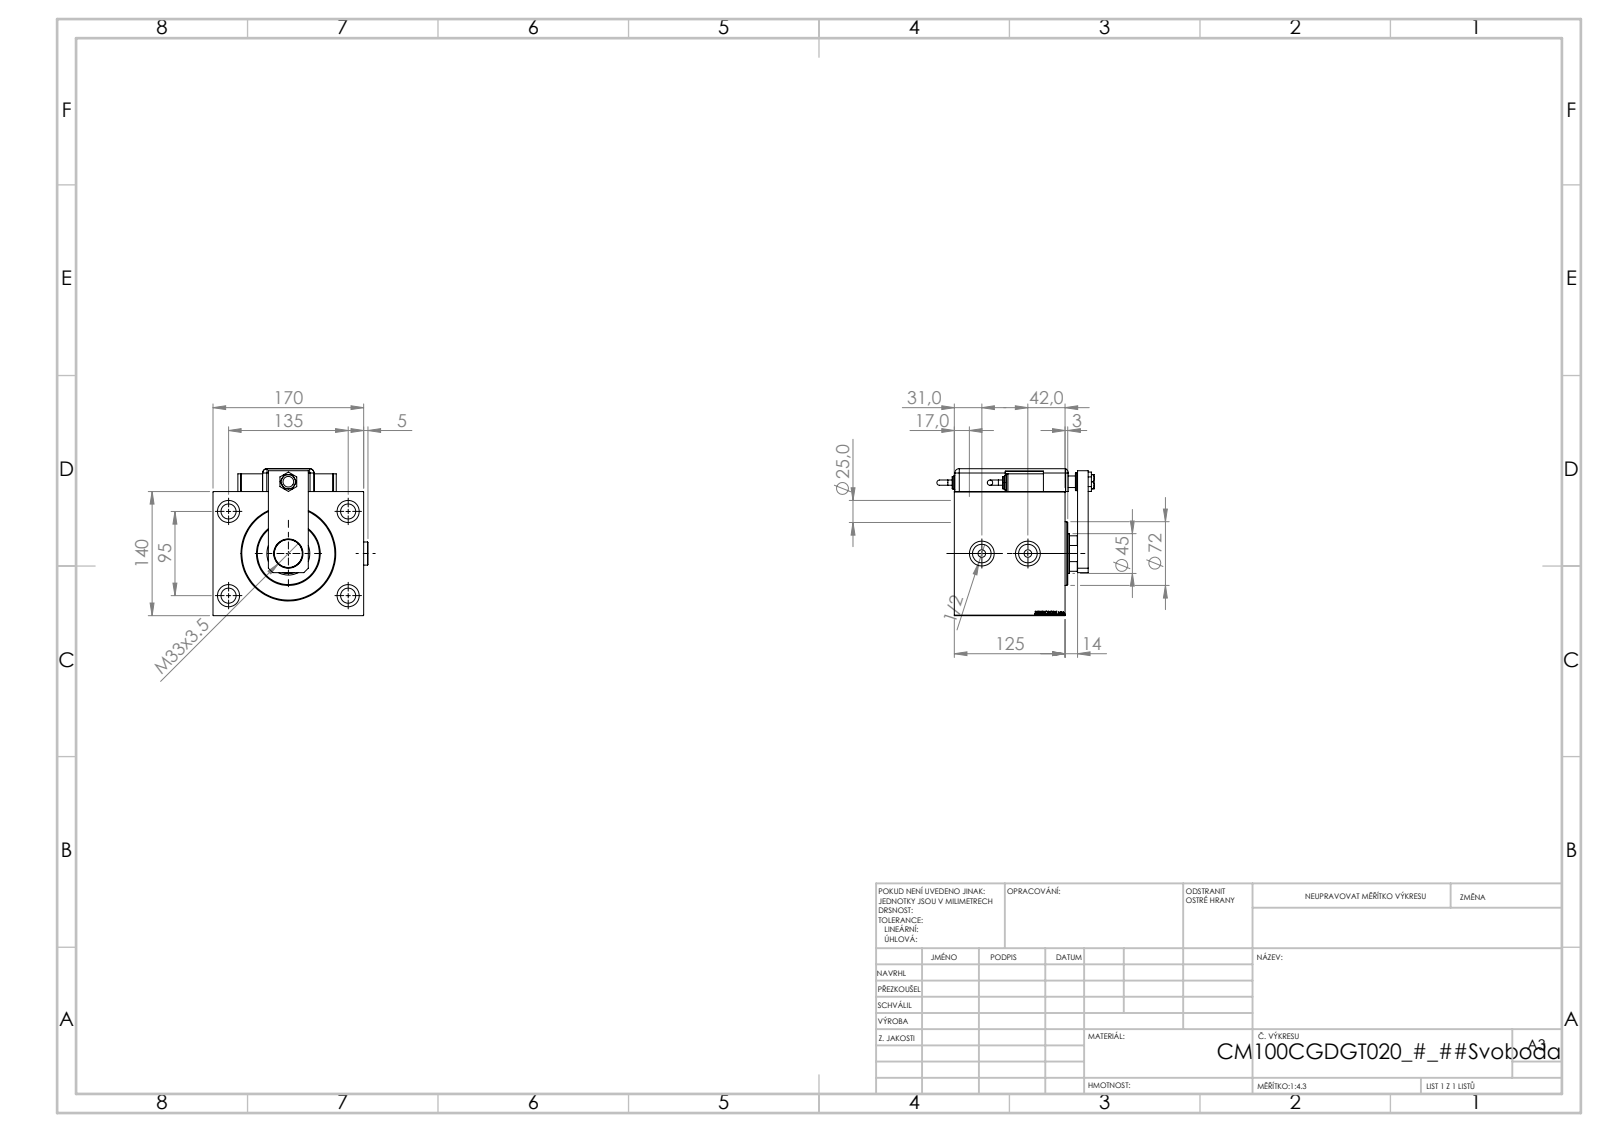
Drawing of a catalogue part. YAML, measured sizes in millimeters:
part_name: "SWITCH Q; V450CM_C_Body; V450CM_VC_B; TYC (+8 more)"
step_written_by: "SolidWorks 2019 (CONFIG_CONTROL_DESIGN)"
units: millimeters
bodies: {solids: 15, faces: 1301, planar: 649, cylindrical: 131, other: 521}
overall_size: [177.66, 174.9, 165.8]
volume: 2923000
surface_area: 306197
round_holes:
  - {diameter: 17, count: 4}
  - {diameter: 25, count: 4}
  - {diameter: 4, count: 2}
  - {diameter: 8, count: 2}
  - {diameter: 8.5, count: 2}
  - {diameter: 20.96, count: 2}
  - {diameter: 28, count: 2}
  - {diameter: 12, count: 1}
  - {diameter: 13, count: 1}
  - {diameter: 14, count: 1}
  - {diameter: 31.5, count: 1}
  - {diameter: 33, count: 1}
round_bosses_or_shafts:
  - {diameter: 20, count: 3}
  - {diameter: 26, count: 2}
  - {diameter: 16, count: 2}
  - {diameter: 14, count: 2}
  - {diameter: 6, count: 2}
  - {diameter: 72, count: 1}
partial_cylinders:
  - {radius: 5, count: 9}
  - {radius: 10, count: 1}
  - {radius: 22, count: 1}
face_to_face_distances: [140, 125, 170, 51, 74, 3, 10, 21.6, 29.4, 103.4]
hole_center_spacings: [82.54, 75.36, 95, 135, 145.15, 165.08, 20, 52]
